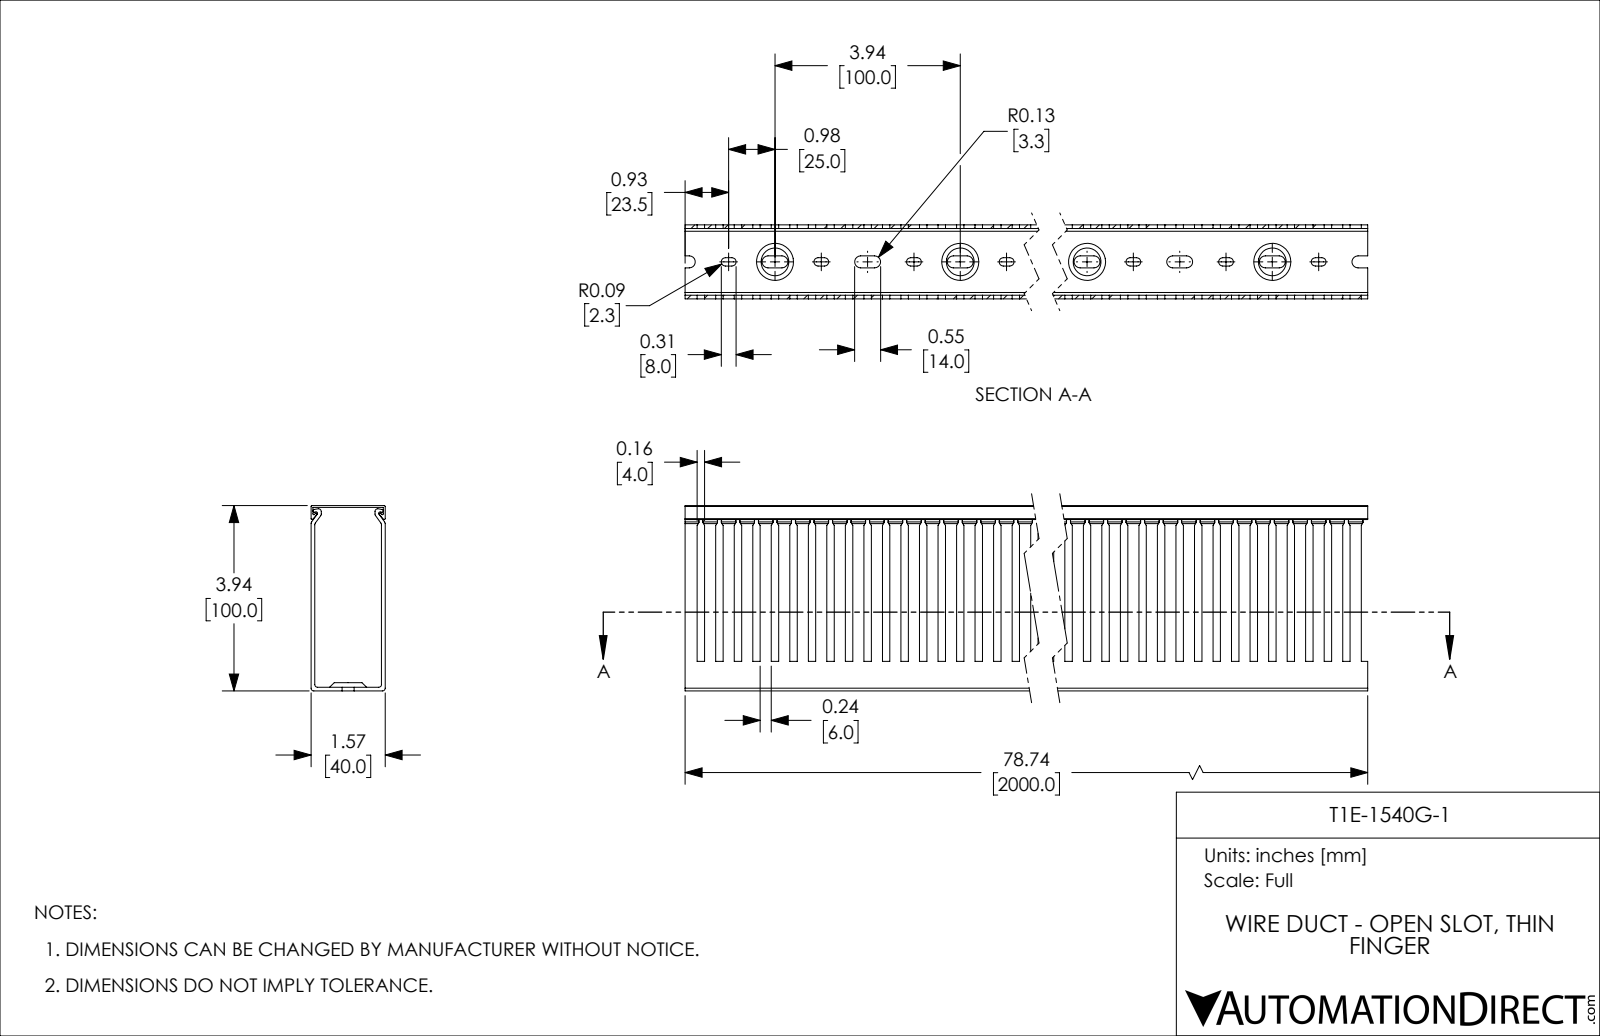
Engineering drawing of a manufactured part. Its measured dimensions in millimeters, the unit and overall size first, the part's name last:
Units: millimetres
Overall size (bounding box): 2000 × 100 × 40
Partial cylindrical surfaces — rounded edges, fillets, slot ends (radius × count): R2.25 ×80, R3.25 ×80, R1.5 ×12, R0.5 ×8, R0.75 ×6
Main face-to-face distances: 2, 38, 40, 36, 1, 99, 100, 97, 98, 39
Volume: 1 056 000 mm³ · Surface area: 1 176 000 mm²
Bodies: 2 solids, 1005 faces (534 planar, 431 cylindrical, 40 other)
Part name (STEP PRODUCT): T1E-1540G-1
STEP written by: SolidWorks 2021 (CONFIG_CONTROL_DESIGN)
